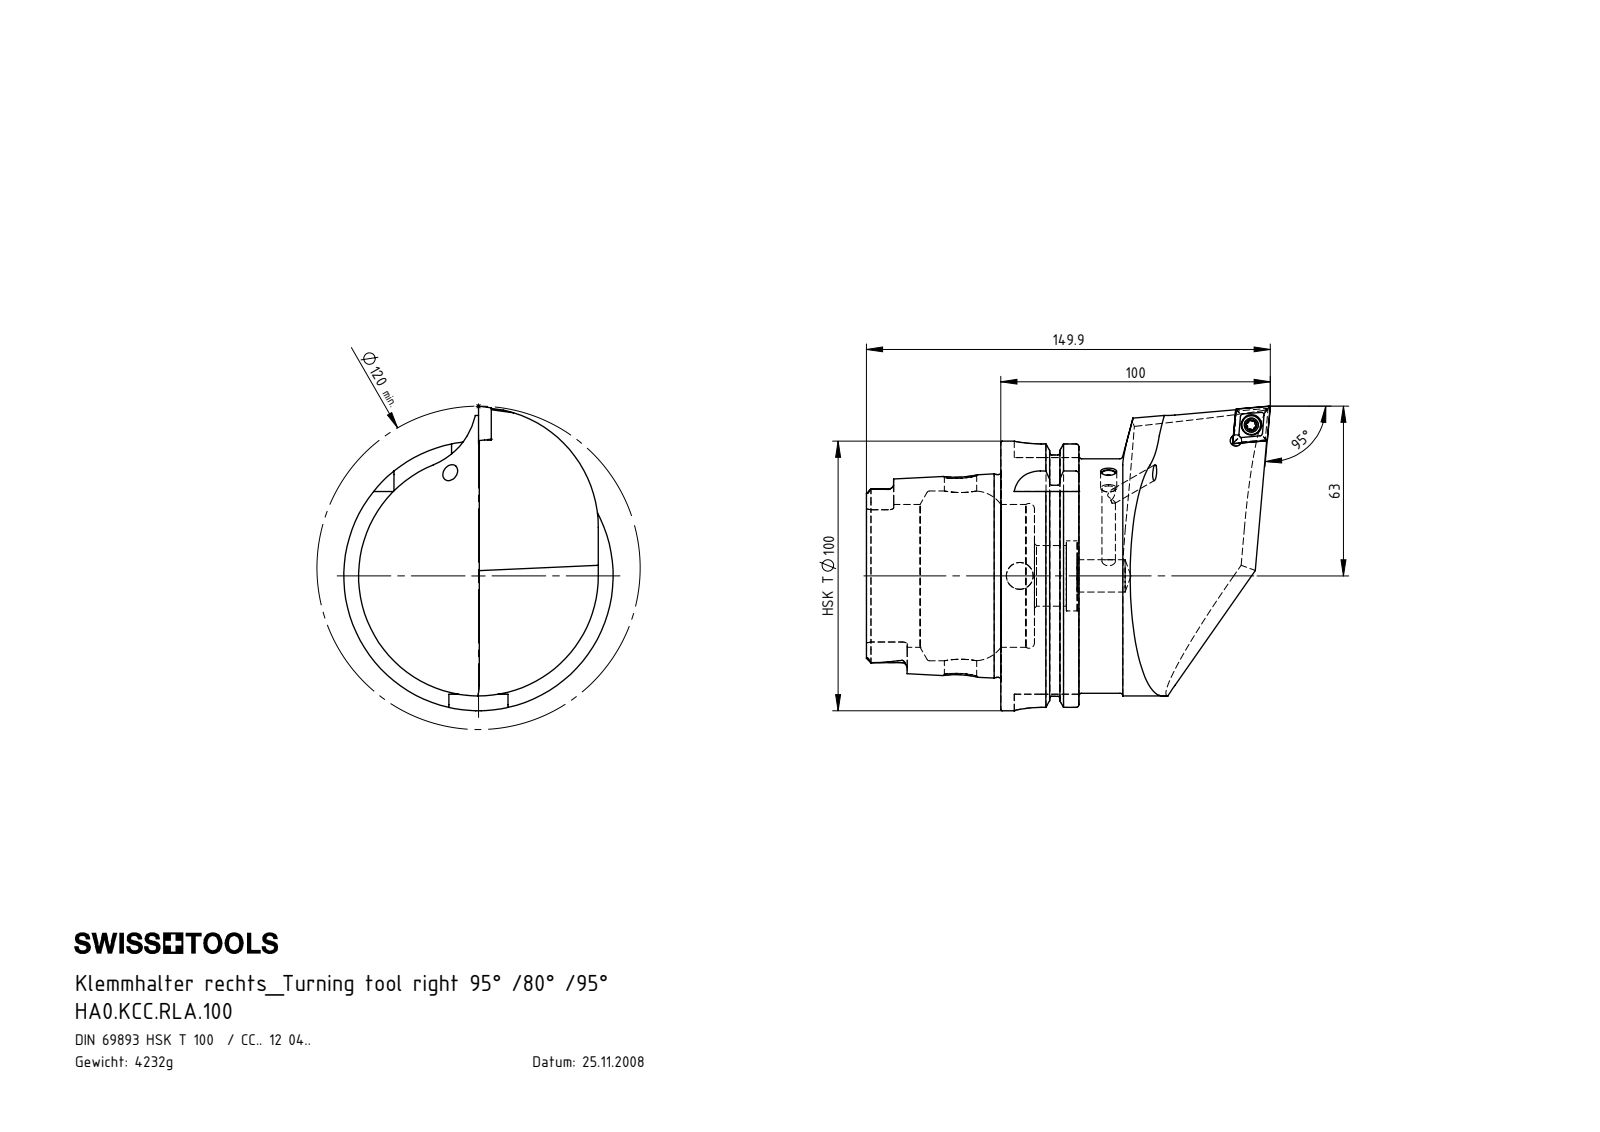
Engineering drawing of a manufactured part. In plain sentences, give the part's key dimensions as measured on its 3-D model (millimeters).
The part is named "HA0.KCC.RLA.100; KVT_MB_600_050; WCC-ER2.001.010_A; CCMT120404 (+1 more)". Its 3-D file was written by "SolidWorks 2012 (CONFIG_CONTROL_DESIGN)". It is 5 solids with 303 faces: 73 planar, 90 cylindrical and 140 other. Overall it measures 149.9 by 113 by 100 millimeters. Its volume is 538 981 cubic millimeters and its surface area 68 932 square millimeters. Round holes: 2 of diameter 4.2, 2 of diameter 12, 1 of diameter 4, 1 of diameter 5, 1 of diameter 5.5, 1 of diameter 6, 1 of diameter 7.6, 1 of diameter 10, 1 of diameter 22.5, 1 of diameter 26, 1 of diameter 53, 1 of diameter 63. Round bosses or shafts: 2 of diameter 5, 1 of diameter 100, 1 of diameter 91.95, 1 of diameter 87, 1 of diameter 75.26, 1 of diameter 7. Partial cylindrical surfaces (rounded edges, fillets, slot ends): 6 of radius 0.39, 6 of radius 0.69, 6 of radius 1.9, 4 of radius 10, 2 of radius 4.83, 2 of radius 4.88, 2 of radius 44.5, 1 of radius 6. The main face-to-face distances are 12.45, 28.95, 16.5, 49.9, 62.35, 78.85, 44.2, 87.8, 78.2, 28.3. The hole center spacings are 8.09, 8.2, 94.68, 102.58, 102.69.
